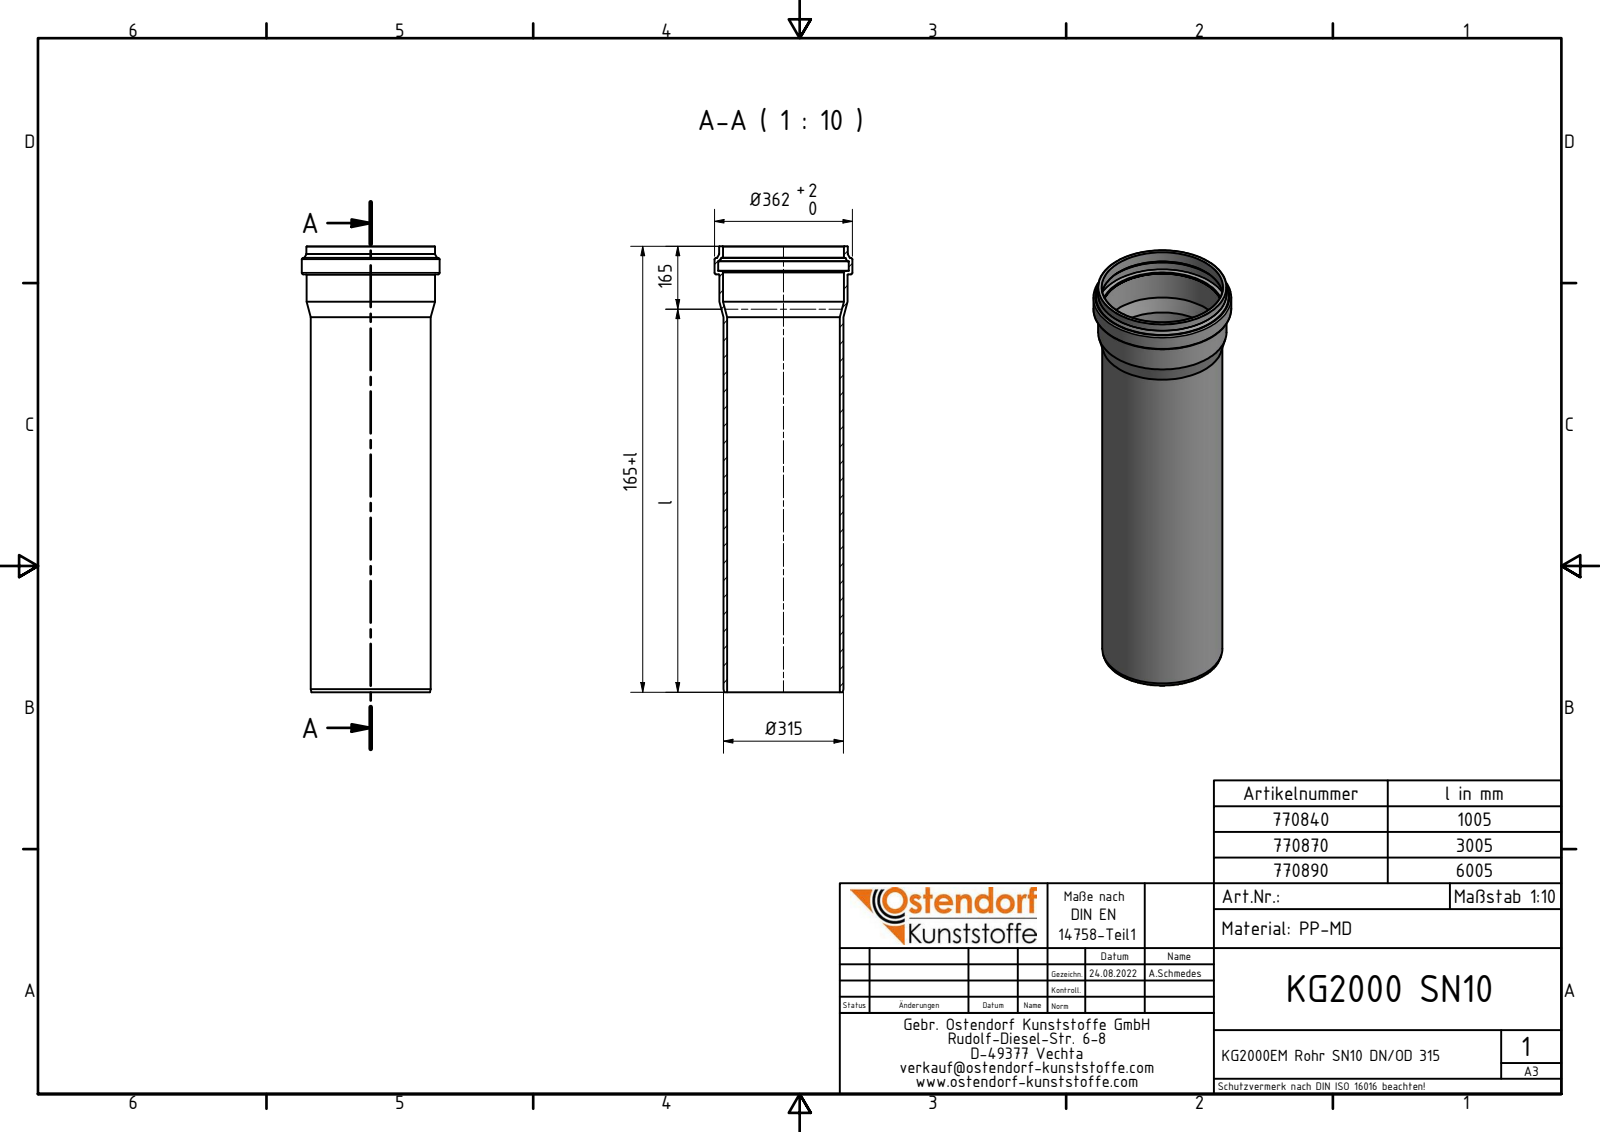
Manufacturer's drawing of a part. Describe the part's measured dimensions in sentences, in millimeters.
The part is named "770840 KG2000EM Rohr SN10 DN_OD 315x1000". Its 3-D file was written by "Autodesk Inventor 2020 (AUTOMOTIVE_DESIGN)". It is 1 solid with 36 faces: 5 planar, 9 cylindrical and 22 other. Overall it measures 1170 by 362 by 362 millimeters. Its volume is 11 540 000 cubic millimeters and its surface area 2 331 000 square millimeters. Round holes: 1 of diameter 295.3, 1 of diameter 317.1, 1 of diameter 317.5, 1 of diameter 343.2. Round bosses or shafts: 1 of diameter 362, 1 of diameter 337.5, 1 of diameter 337.1, 1 of diameter 315.3. The main face-to-face distances are 73.5, 1096.5, 1170, 1139.7, 43.2, 30.3, 1101.46, 4.96, 38.24, 68.54.
